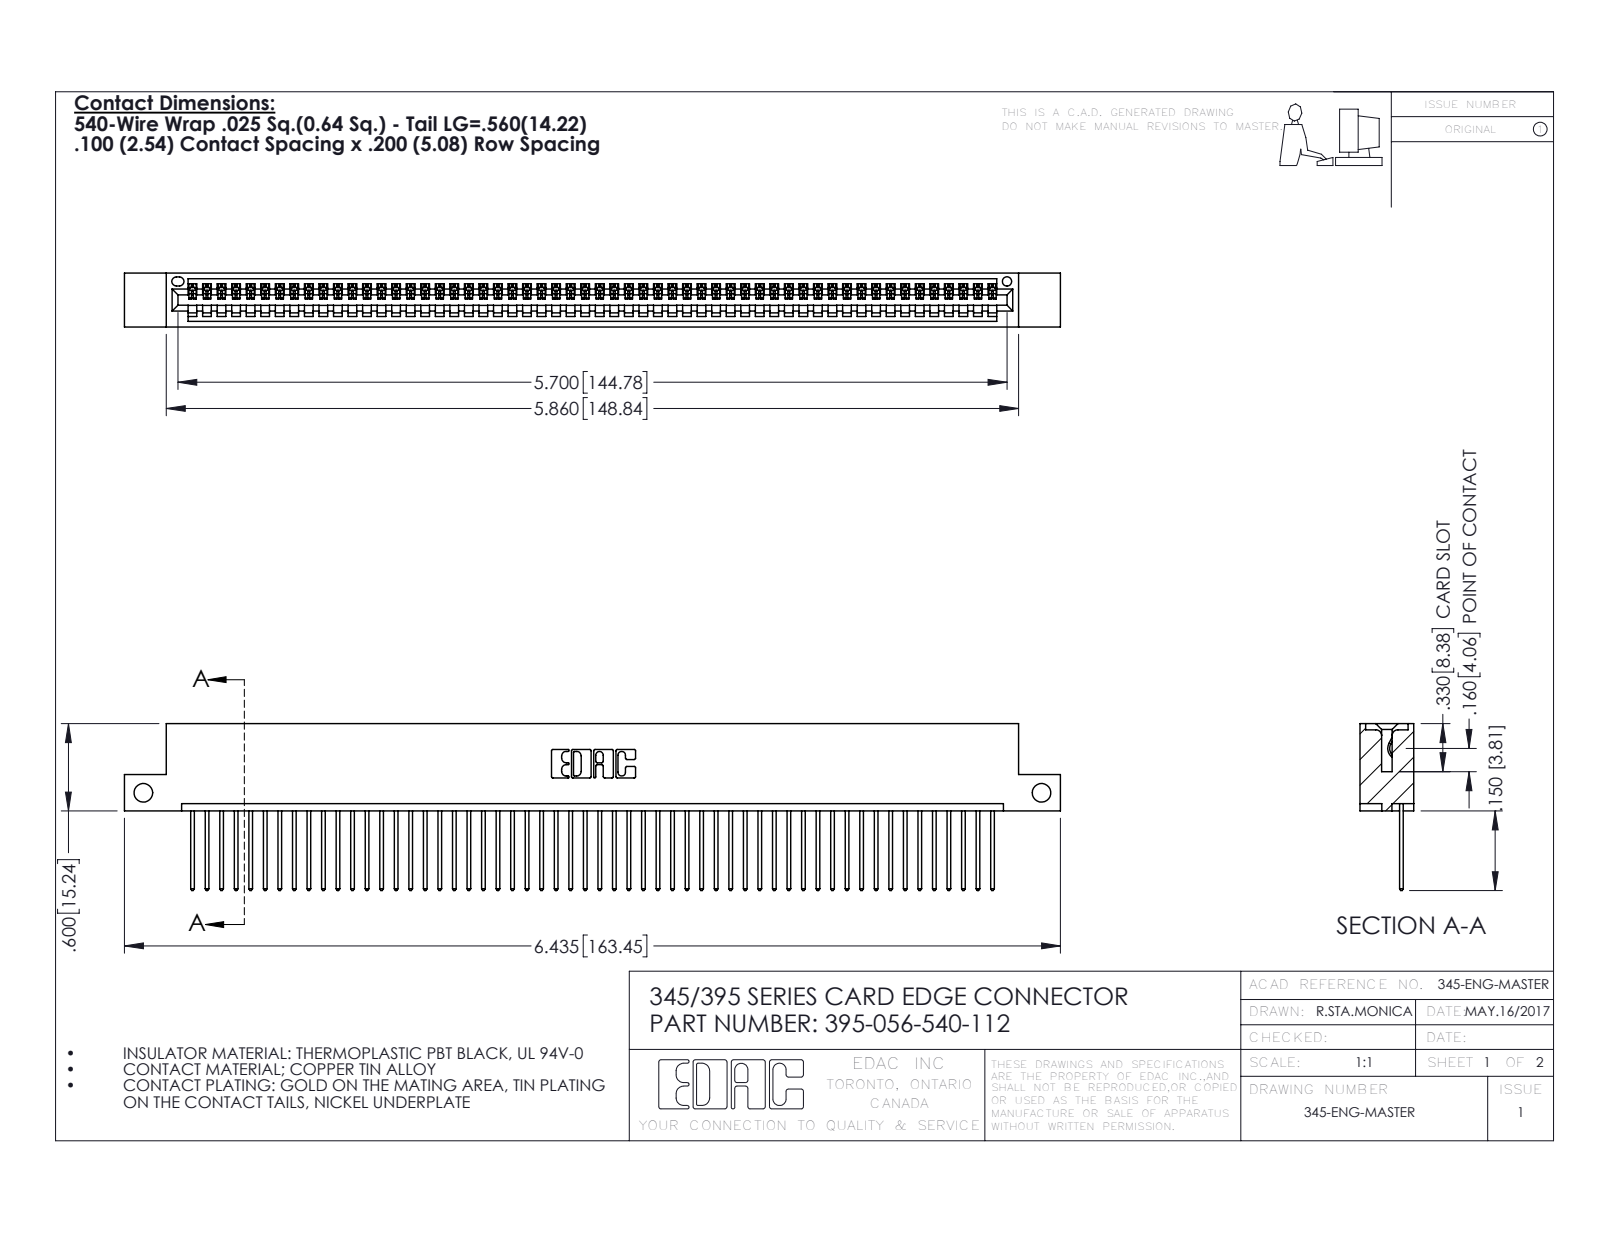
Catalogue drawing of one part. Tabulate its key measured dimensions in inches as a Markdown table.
| quantity | value |
| --- | --- |
| part name | 345 Part_Flush Mounting Lugs - Side Mount; 345-292-001_345-293-140; 395-056-540-112 |
| STEP written by | SolidWorks 2016 (CONFIG_CONTROL_DESIGN) |
| units | inches |
| bodies | 57 solids, 3374 faces (2320 planar, 1054 cylindrical, 0 other) |
| overall size | 6.435 × 1.147 × 0.37 |
| volume | 0.954 in³ |
| surface area | 33.11 in² |
| round holes (diameter × count) | 0.128 × 2, 0.064 × 1 |
| partial cylindrical surfaces (radius × count) | 0.006 × 112, 0.01 × 112, 0.01 × 22, 0.007 × 6, 0.031 × 6, 0.026 × 3, 0.031 × 2, 0.04 × 2 |
| main face-to-face distances | 0.298, 0.072, 0.37, 0.098, 0.272, 0.025, 0.2, 0.225, 0.149, 0.072 |
| hole center spacings | 6.175 |
